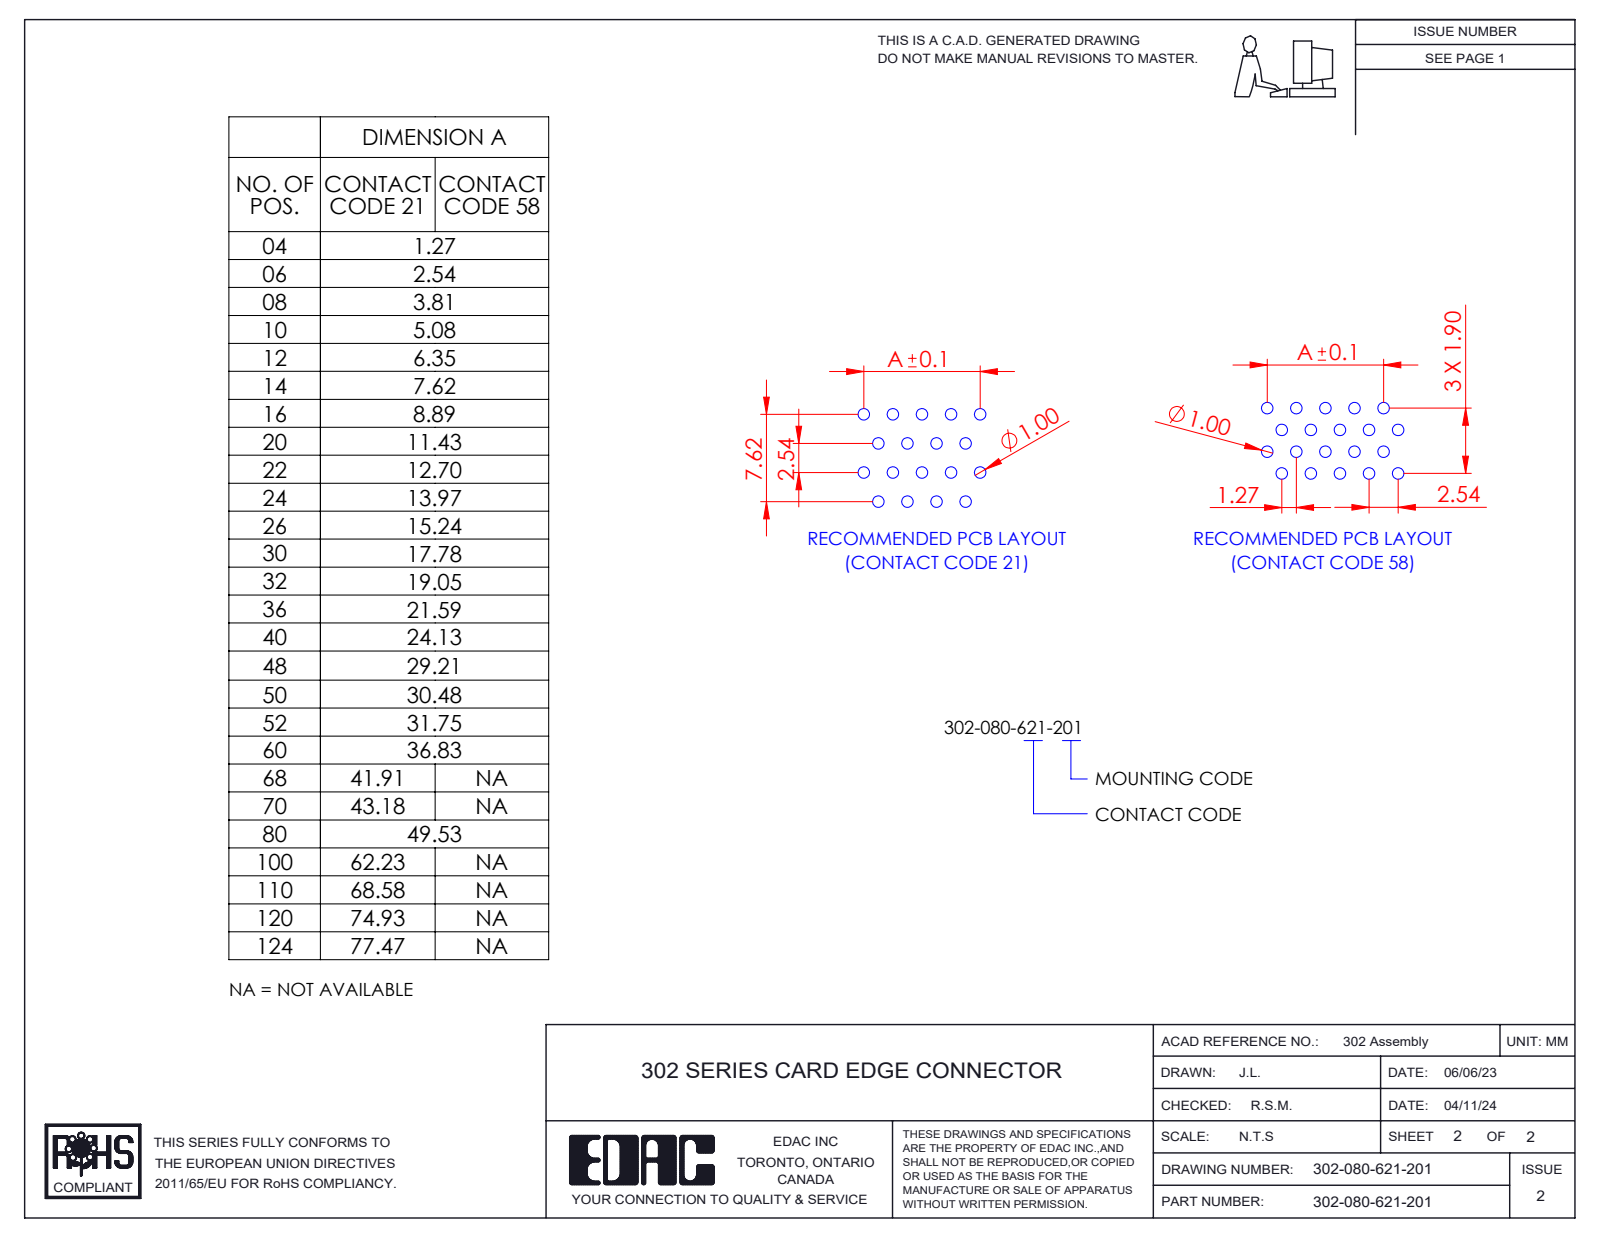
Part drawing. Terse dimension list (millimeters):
name: Contact_302-290-X21 (1); 302-080-621-201; Contact_302-290-X21 (2); HSG_Vertical HSG
written by: SolidWorks 2023 (CONFIG_CONTROL_DESIGN)
unit: mm
bodies: 81 solids, 3706 faces (2729 planar, 813 cylindrical, 164 other)
size: 56.9 × 17.63 × 8.88
volume: 4 394 mm³; area: 12 188 mm²
rounds: 88× R0.2, 4× R2.03, 4× R2.09, 2× R0.11, 2× R0.4, 2× R0.41, 2× R1.25, 2× R1.53
face distances: 2.54, 1.27, 5.08, 3.81, 7.62, 6.35, 8.88, 8.89, 10.16, 11.43
